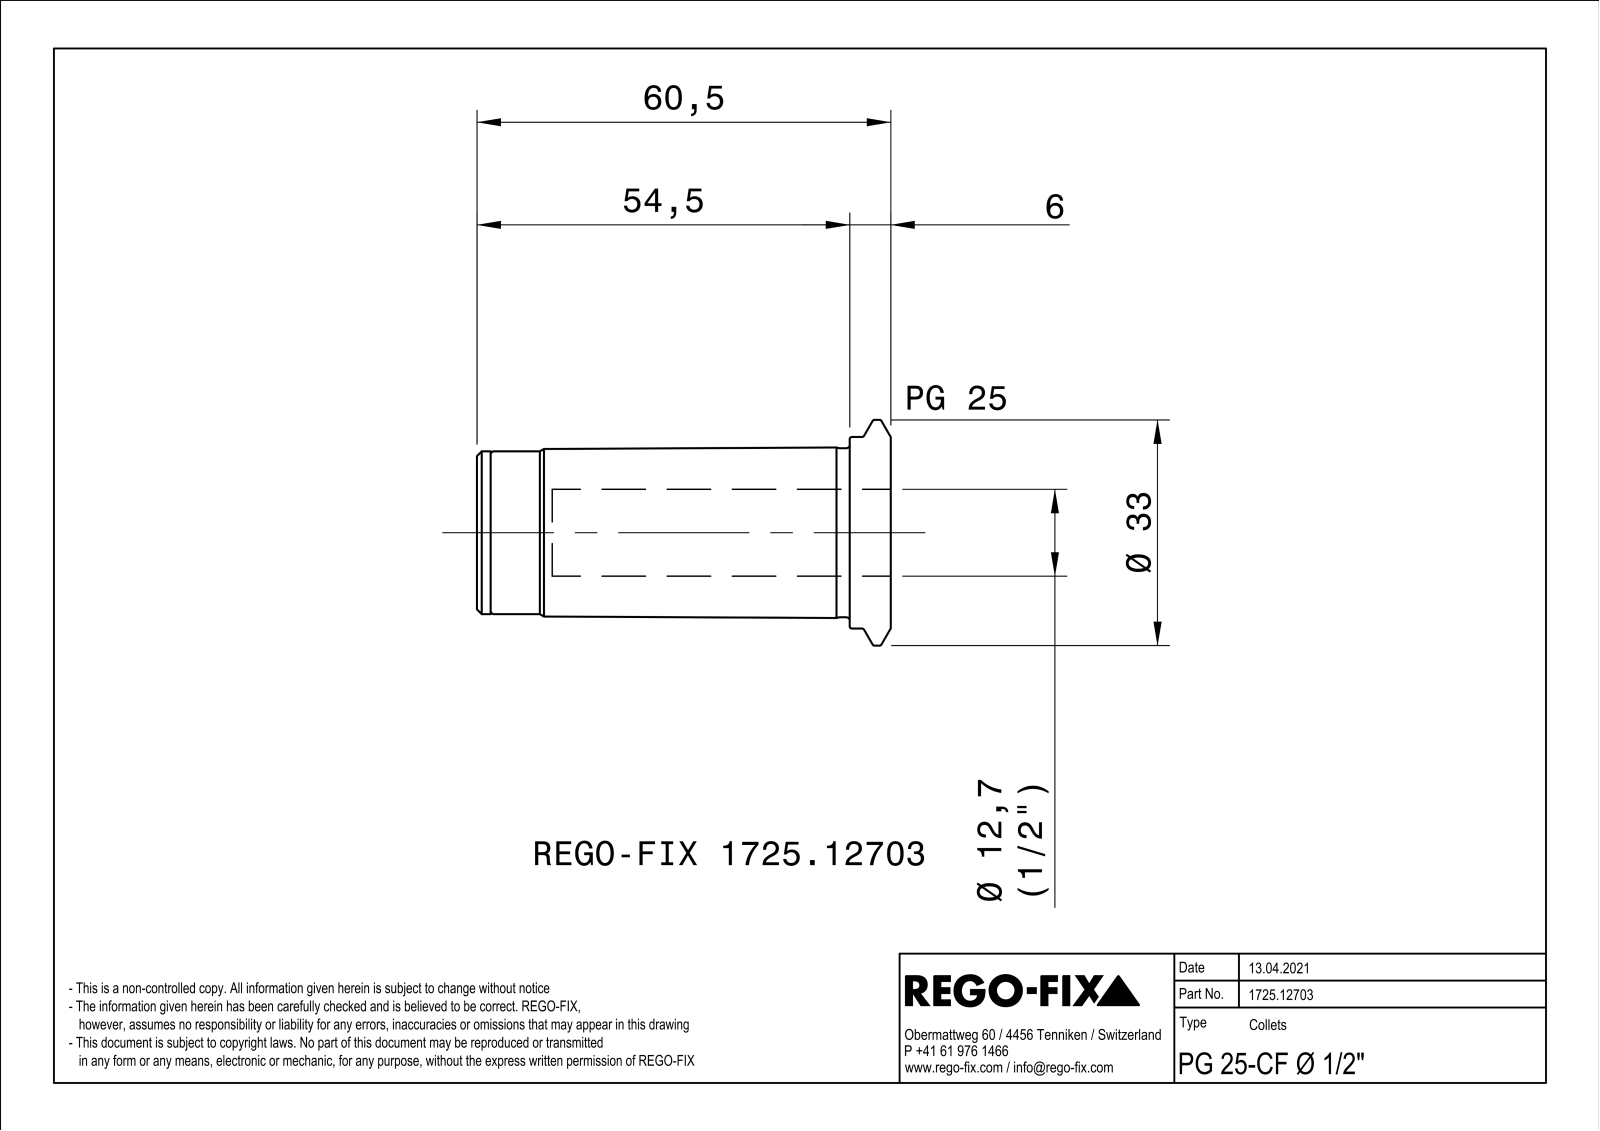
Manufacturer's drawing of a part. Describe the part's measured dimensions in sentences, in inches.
The part is named "NOCUT". Its 3-D file was written by "SIEMENS PLM Software Solid Edge ST10 (AUTOMOTIVE_DESIGN)". It is 1 solid with 89 faces: 23 planar, 27 cylindrical and 39 other. Overall it measures 2.382 by 1.299 by 1.299 inches. Its volume is 1.315 cubic inches and its surface area 17.35 square inches. Round holes: 3 of diameter 0.098, 1 of diameter 0.205, 1 of diameter 0.272, 1 of diameter 0.323, 1 of diameter 0.5, 1 of diameter 0.824, 1 of diameter 0.874. Round bosses or shafts: 1 of diameter 1.299, 1 of diameter 1.102, 1 of diameter 0.972, 1 of diameter 0.937, 1 of diameter 0.803, 1 of diameter 0.472. Partial cylindrical surfaces (rounded edges, fillets, slot ends): 3 of radius 0.03. The main face-to-face distances are 0.039, 2.382, 2.071, 0.311, 2.303, 0.232, 0.079, 1.969, 0.102, 0.335. The hole center spacings are 0.305, 0.529, 0.528.
